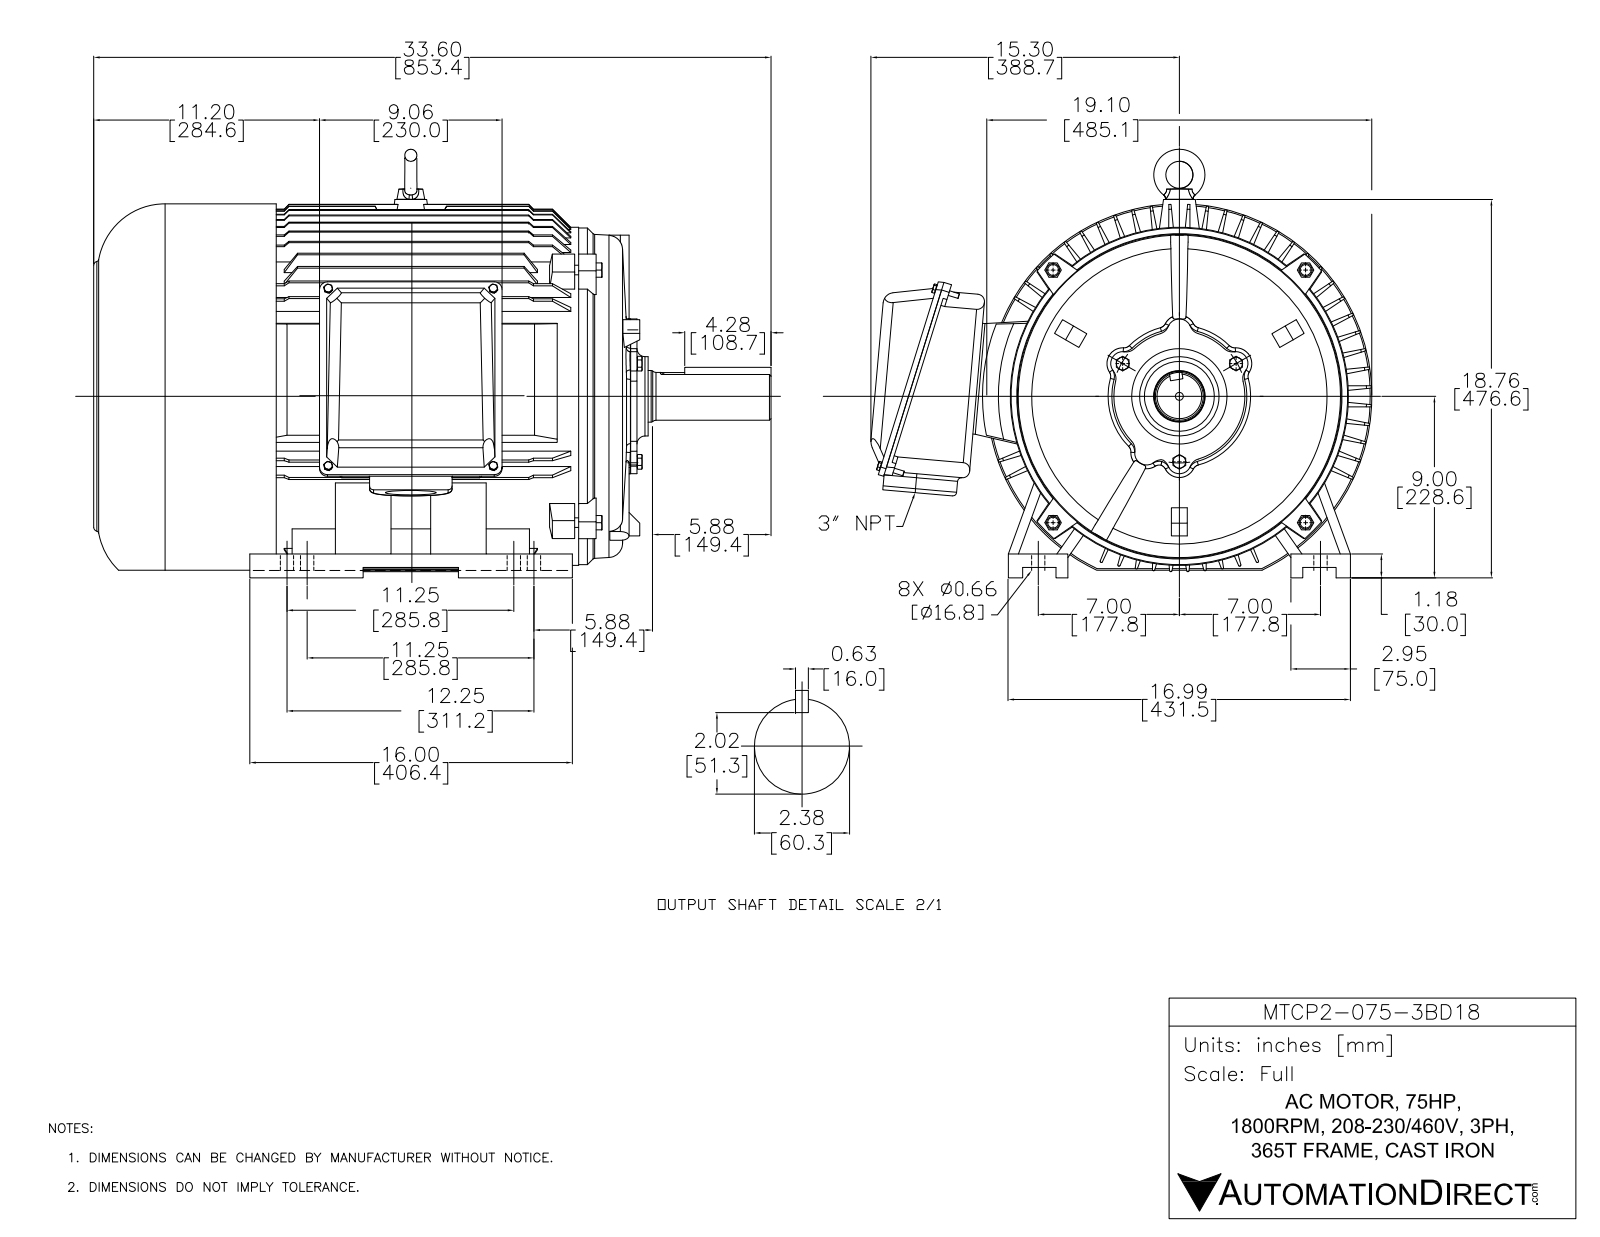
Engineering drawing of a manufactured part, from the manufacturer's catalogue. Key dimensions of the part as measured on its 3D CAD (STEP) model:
Part name (STEP PRODUCT): PEWWE-365T-4,6,8
STEP written by: SolidWorks 2017 (AUTOMOTIVE_DESIGN)
Units: inches
Bodies: 19 solids, 2734 faces (2022 planar, 349 cylindrical, 363 other)
Overall size (bounding box): 33.599 × 24.85 × 21.252
Volume: 4 406 in³ · Surface area: 6 003 in²
Round holes (diameter × count): ⌀0.669 ×8, ⌀0.472 ×7, ⌀0.236 ×4, ⌀0.315 ×4, ⌀0.335 ×4, ⌀0.394 ×4, ⌀0.539 ×4, ⌀0.453 ×1, ⌀0.551 ×1, ⌀2.52 ×1, ⌀3.465 ×1, ⌀15.512 ×1
Round bosses / shafts (diameter × count): ⌀0.428 ×4, ⌀0.236 ×4, ⌀0.394 ×3, ⌀19.094 ×1, ⌀16.772 ×1, ⌀16.693 ×1, ⌀16.142 ×1, ⌀7.677 ×1
Partial cylindrical surfaces — rounded edges, fillets, slot ends (radius × count): R0.591 ×25, R0.059 ×8, R0.394 ×8, R0.157 ×4, R0.197 ×4, R0.354 ×4, R0.551 ×4, R0.315 ×3
Main face-to-face distances: 16.654, 0.079, 23.9, 7.246, 0.197, 23.979, 7.325, 0.236, 0.669, 12.303
Hole centre spacings: 8.189, 1, 3.937, 8.858, 9.213, 11.252, 12.326, 12.528
